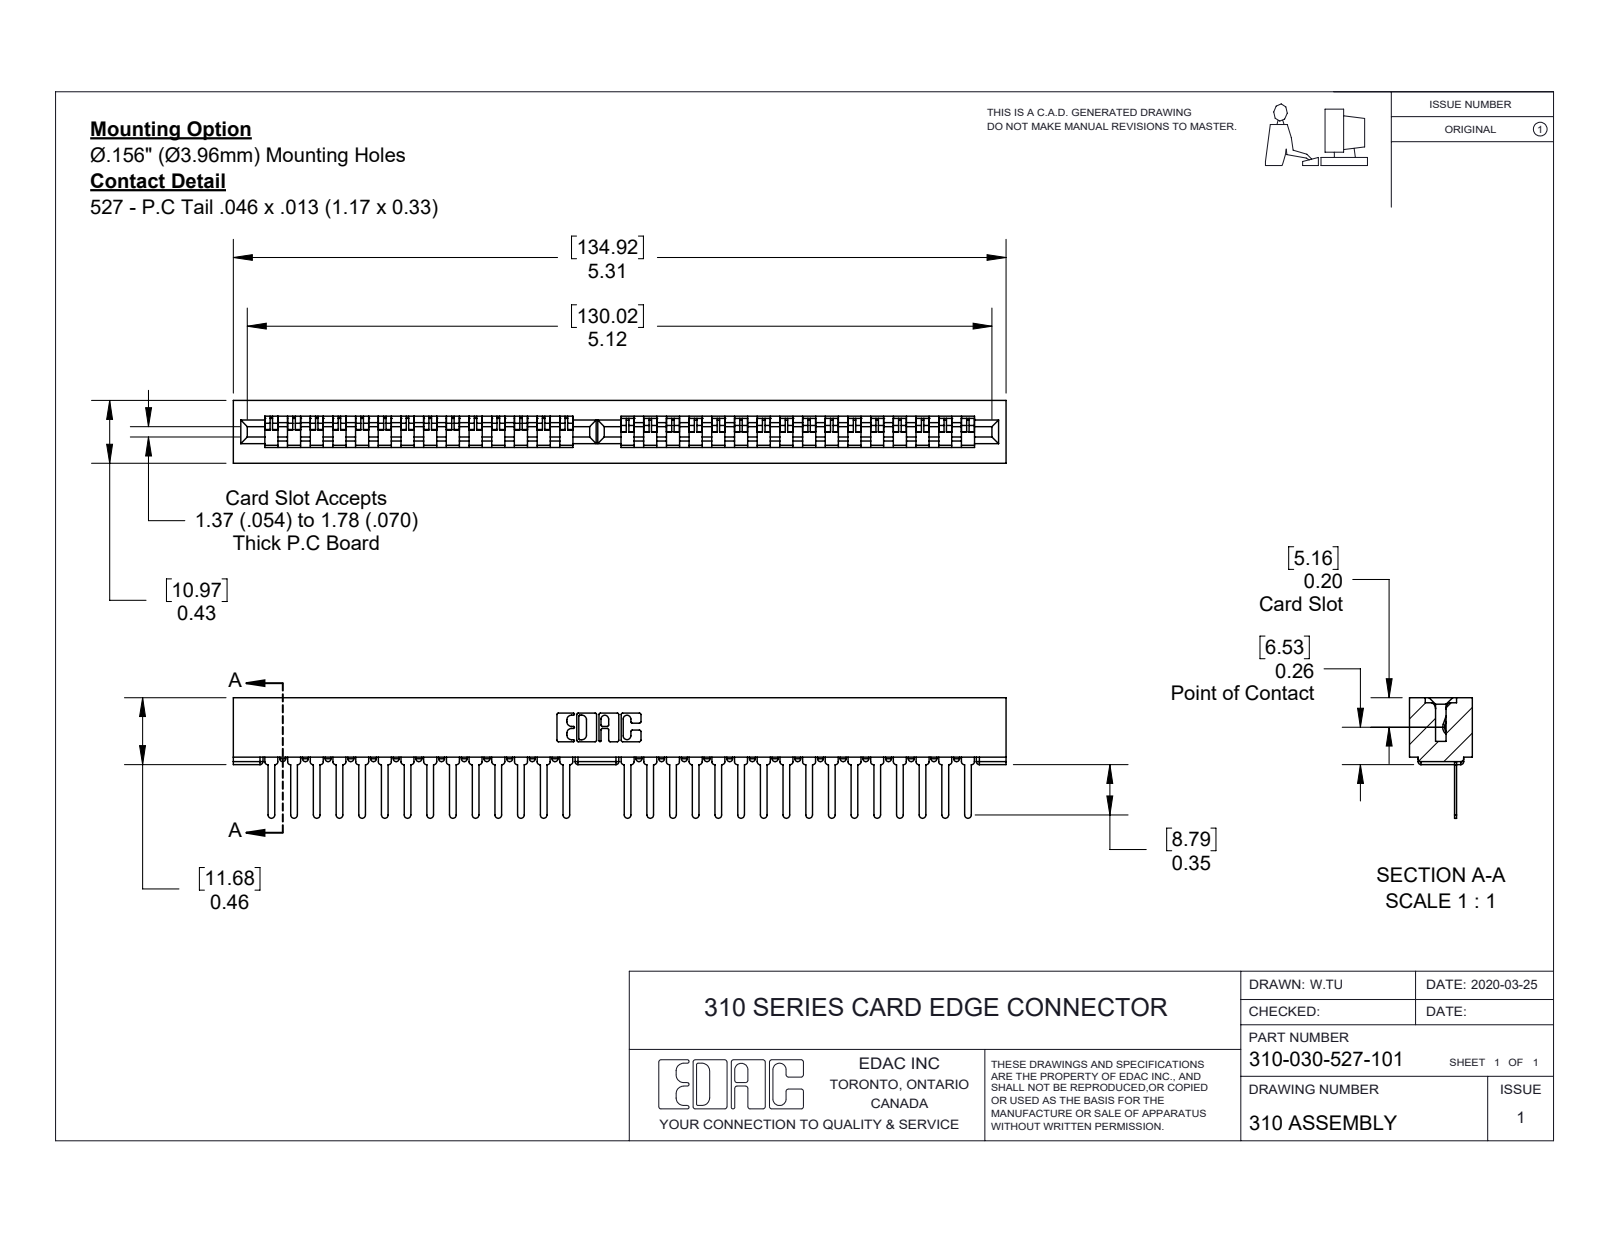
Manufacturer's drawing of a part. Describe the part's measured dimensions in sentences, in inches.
The part is named "310-030-527-101; 310 Part_No Mounting Lugs; 307-290-001_527". Its 3-D file was written by "SolidWorks 2016 (CONFIG_CONTROL_DESIGN)". It is 31 solids with 1838 faces: 1190 planar, 584 cylindrical and 64 other. Overall it measures 5.312 by 0.829 by 0.432 inches. Its volume is 0.713 cubic inches and its surface area 22.01 square inches. Partial cylindrical surfaces (rounded edges, fillets, slot ends): 158 of radius 0.02, 30 of radius 0.023, 22 of radius 0.01, 6 of radius 0.007, 6 of radius 0.031, 3 of radius 0.026, 2 of radius 0.012, 2 of radius 0.025. The main face-to-face distances are 0.109, 0.324, 0.432, 0.015, 0.013, 0.072, 0.409, 0.215, 0.124, 0.309.
